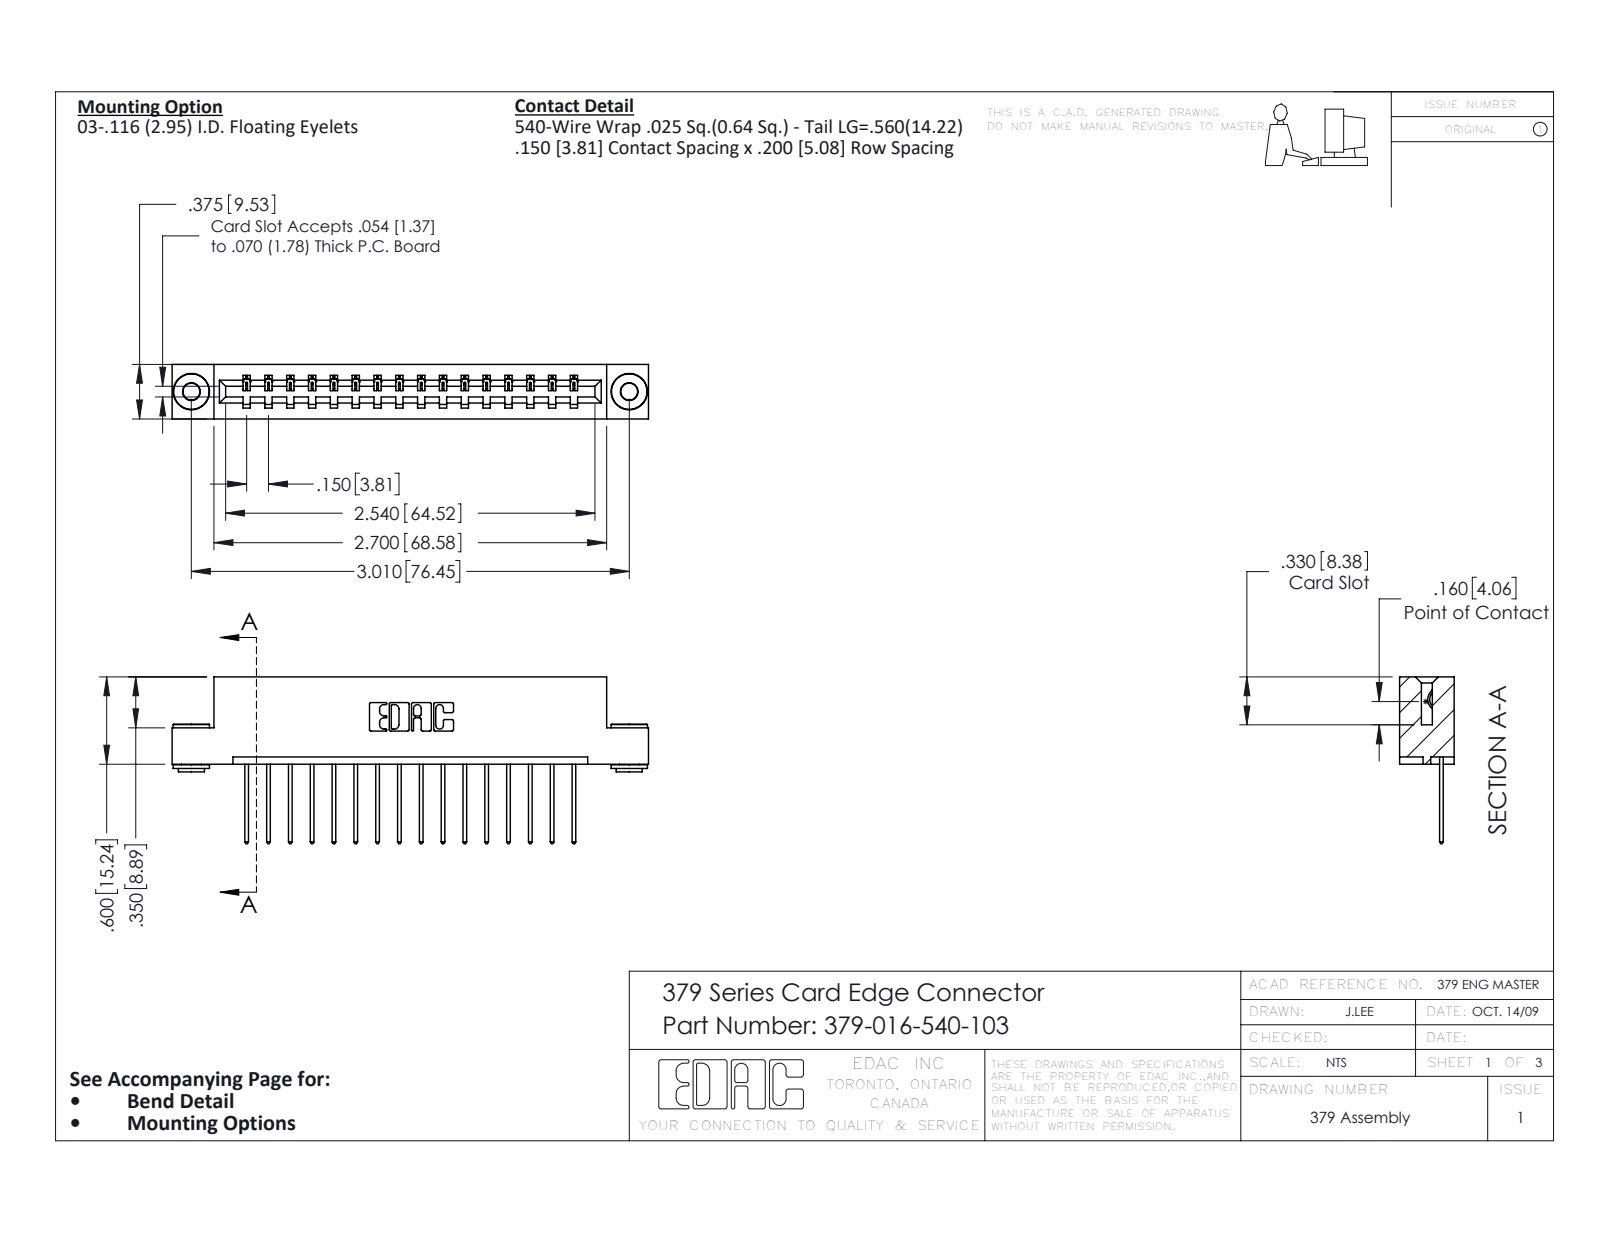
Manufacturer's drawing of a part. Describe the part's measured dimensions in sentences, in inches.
The part is named "379 Part_Flush - .156 Dia - TH; 345-250-002_345-250-002-102; 345-292-001_345-293-140; 379-016-540-103". Its 3-D file was written by "SolidWorks 2020 (CONFIG_CONTROL_DESIGN)". It is 19 solids with 1080 faces: 752 planar, 320 cylindrical and 8 other. Overall it measures 3.275 by 1.147 by 0.375 inches. Its volume is 0.517 cubic inches and its surface area 13.84 square inches. Round holes: 2 of diameter 0.116, 2 of diameter 0.156. Round bosses or shafts: 2 of diameter 0.25, 2 of diameter 0.18, 2 of diameter 0.136. Partial cylindrical surfaces (rounded edges, fillets, slot ends): 32 of radius 0.006, 32 of radius 0.01, 22 of radius 0.01, 6 of radius 0.007, 6 of radius 0.031, 3 of radius 0.026, 1 of radius 0.014, 1 of radius 0.022. The main face-to-face distances are 0.3, 0.075, 0.375, 0.6, 0.15, 0.225, 0.2, 0.45, 0.275, 0.025. The hole center spacings are 3.01.
